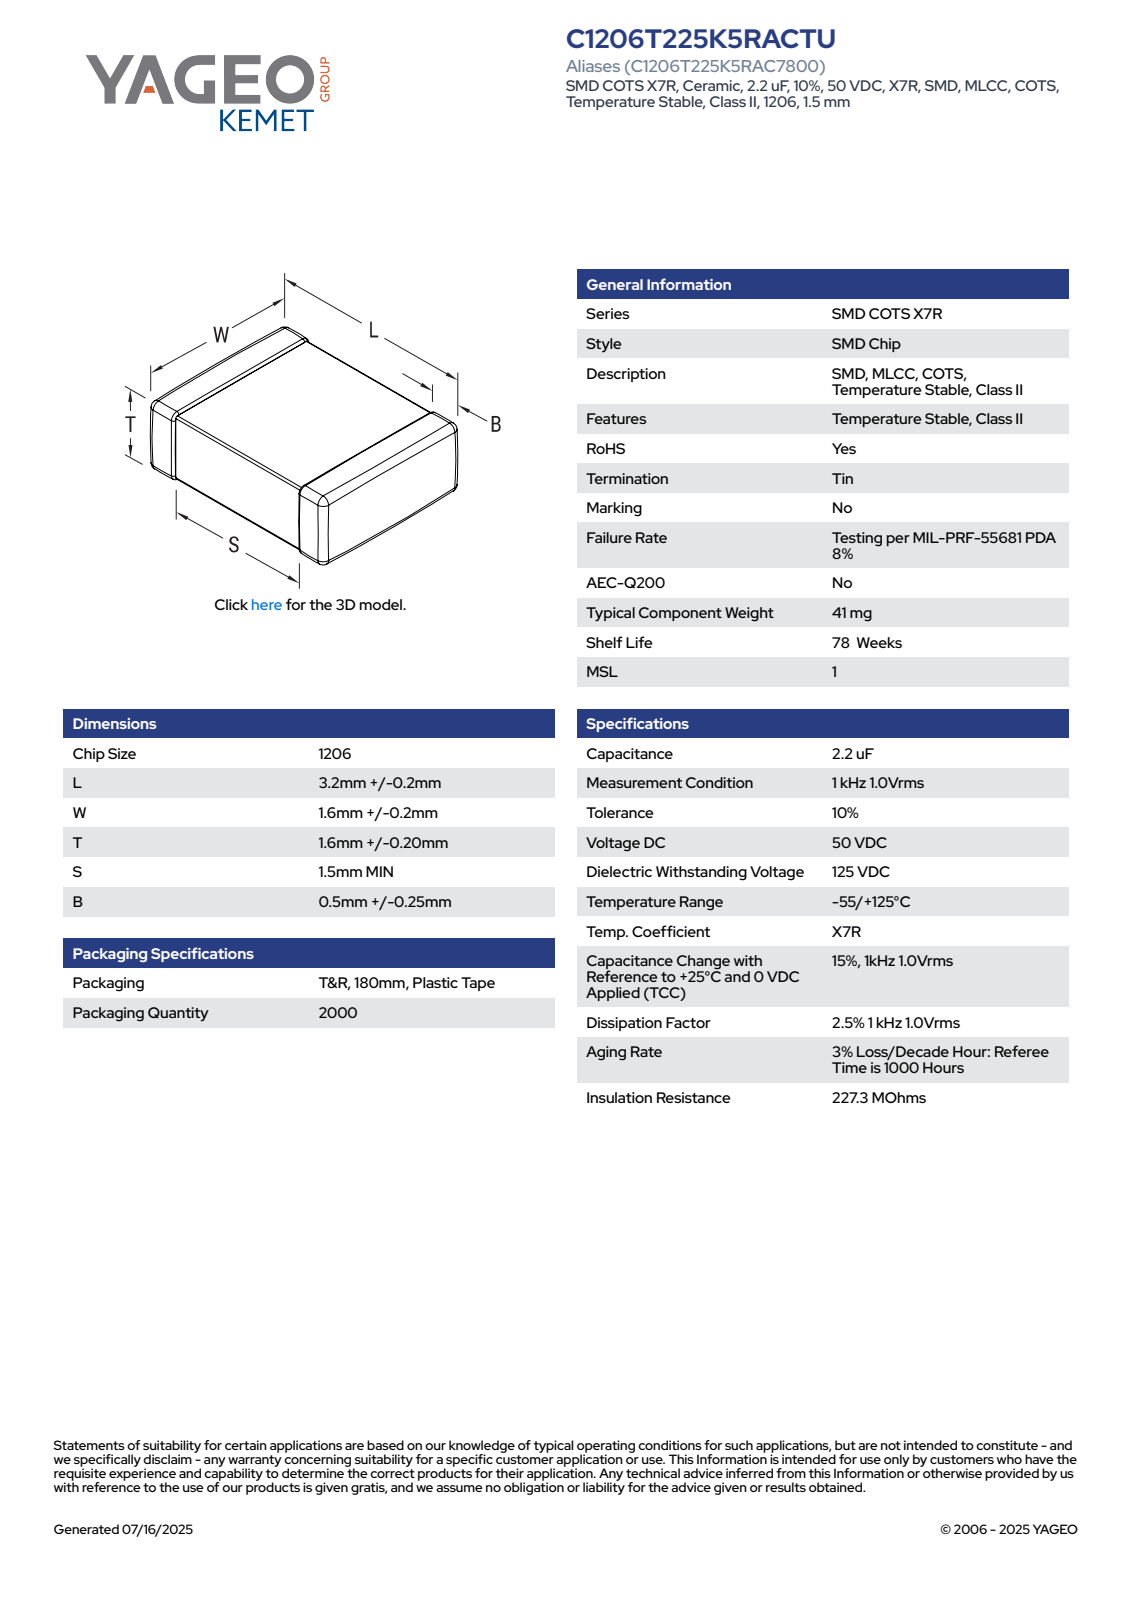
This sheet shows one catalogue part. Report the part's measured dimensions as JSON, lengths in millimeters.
{"part_name": "CCSM_STD_1206_L3.4W1.8T1.8S1.6B0.75", "step_written_by": "SolidWorks 2021 (AUTOMOTIVE_DESIGN)", "units": "millimeters", "bodies": {"solids": 4, "faces": 125, "planar": 71, "cylindrical": 38, "other": 16}, "overall_size": [3.4, 1.8, 1.8], "volume_mm3": 11, "surface_area_mm2": 31, "face_to_face_distances": [1.76, 1.72, 1.8, 3.4, 1.73, 1.77, 1.57, 1.83, 1.84, 1.56]}
